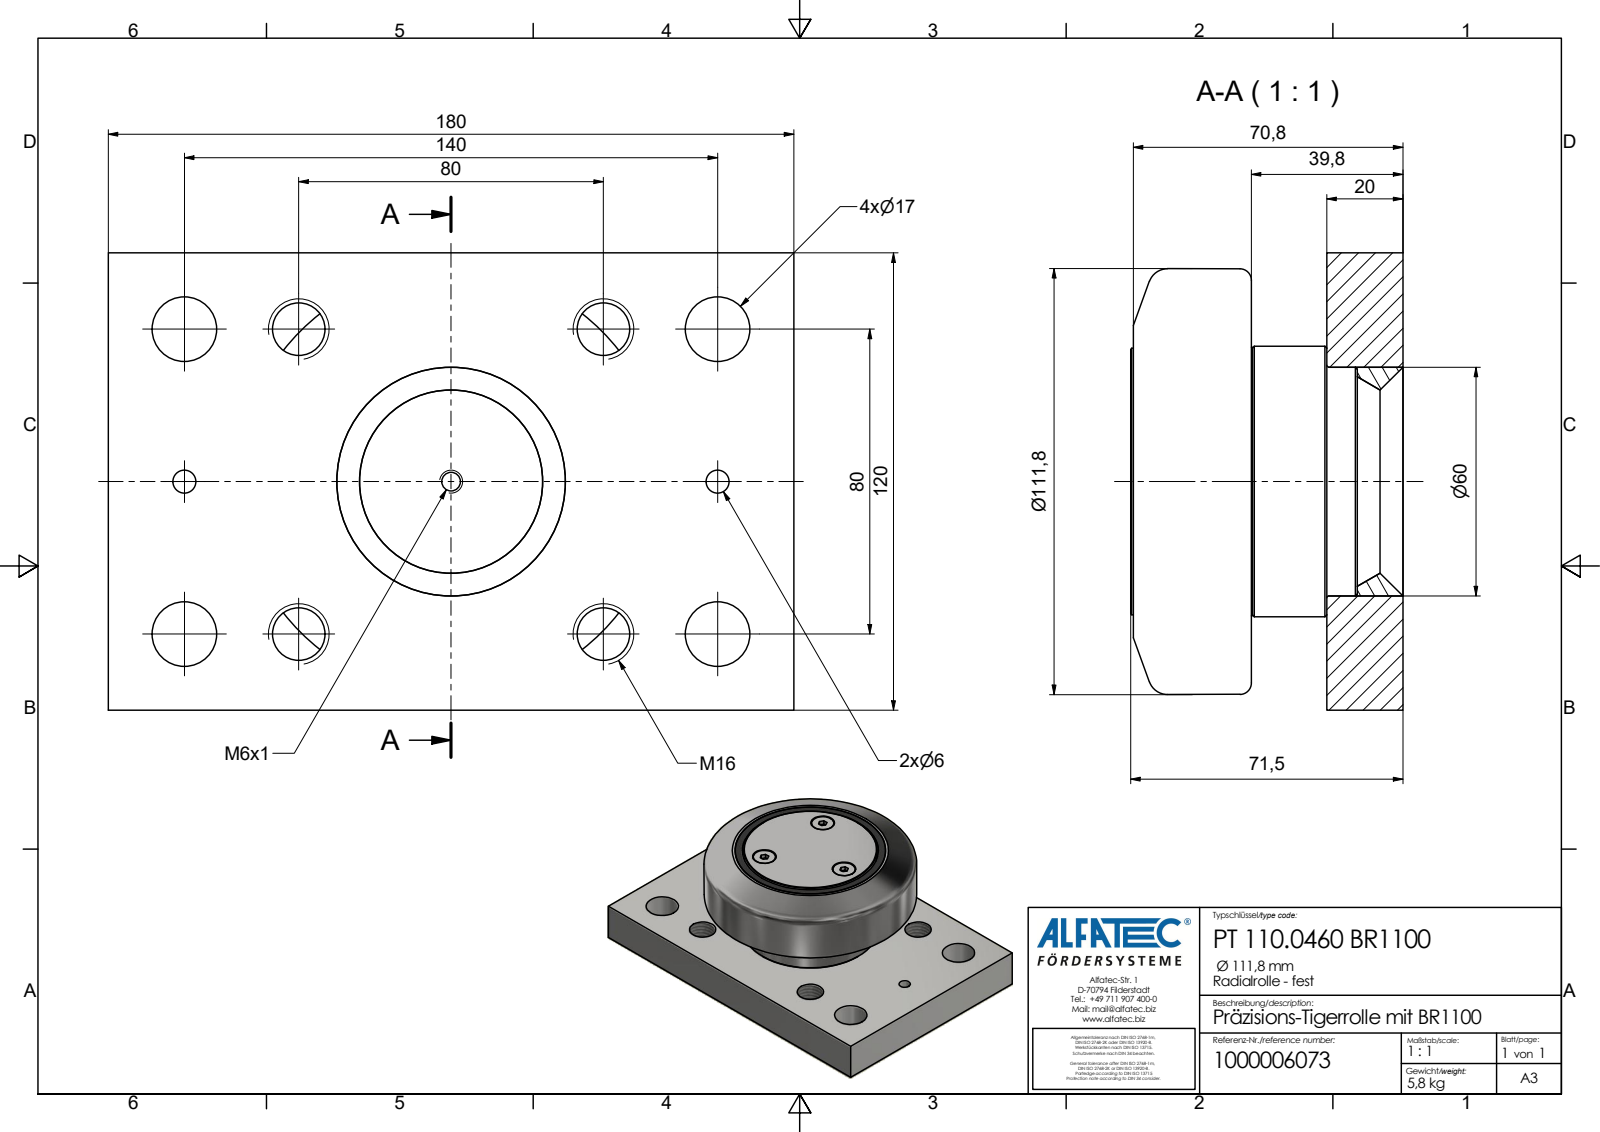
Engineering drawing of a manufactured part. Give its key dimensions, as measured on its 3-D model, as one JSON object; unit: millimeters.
{"part_name": "PT 110.0460 BR1100_Kontur", "step_written_by": "Autodesk Inventor 2020 (AP242_MANAGED_MODEL_BASED_3D_ENGINEERING_MIM_LF)", "units": "millimeters", "bodies": {"solids": 1, "faces": 63, "planar": 37, "cylindrical": 19, "other": 7}, "overall_size": [180, 120, 71.5], "volume_mm3": 771290, "surface_area_mm2": 85744, "round_holes": [[13.84, 4], [17, 4], [12.4, 3], [6, 2]], "round_bosses_or_shafts": [[11.7, 3], [71, 1], [70.5, 1], [70, 1]], "face_to_face_distances": [20, 39.8, 19.8, 120, 71.5, 51.5, 31.7, 180, 70.8, 50.8], "hole_center_spacings": [80, 30, 40, 50, 85.44, 110, 117.05, 136.01]}
